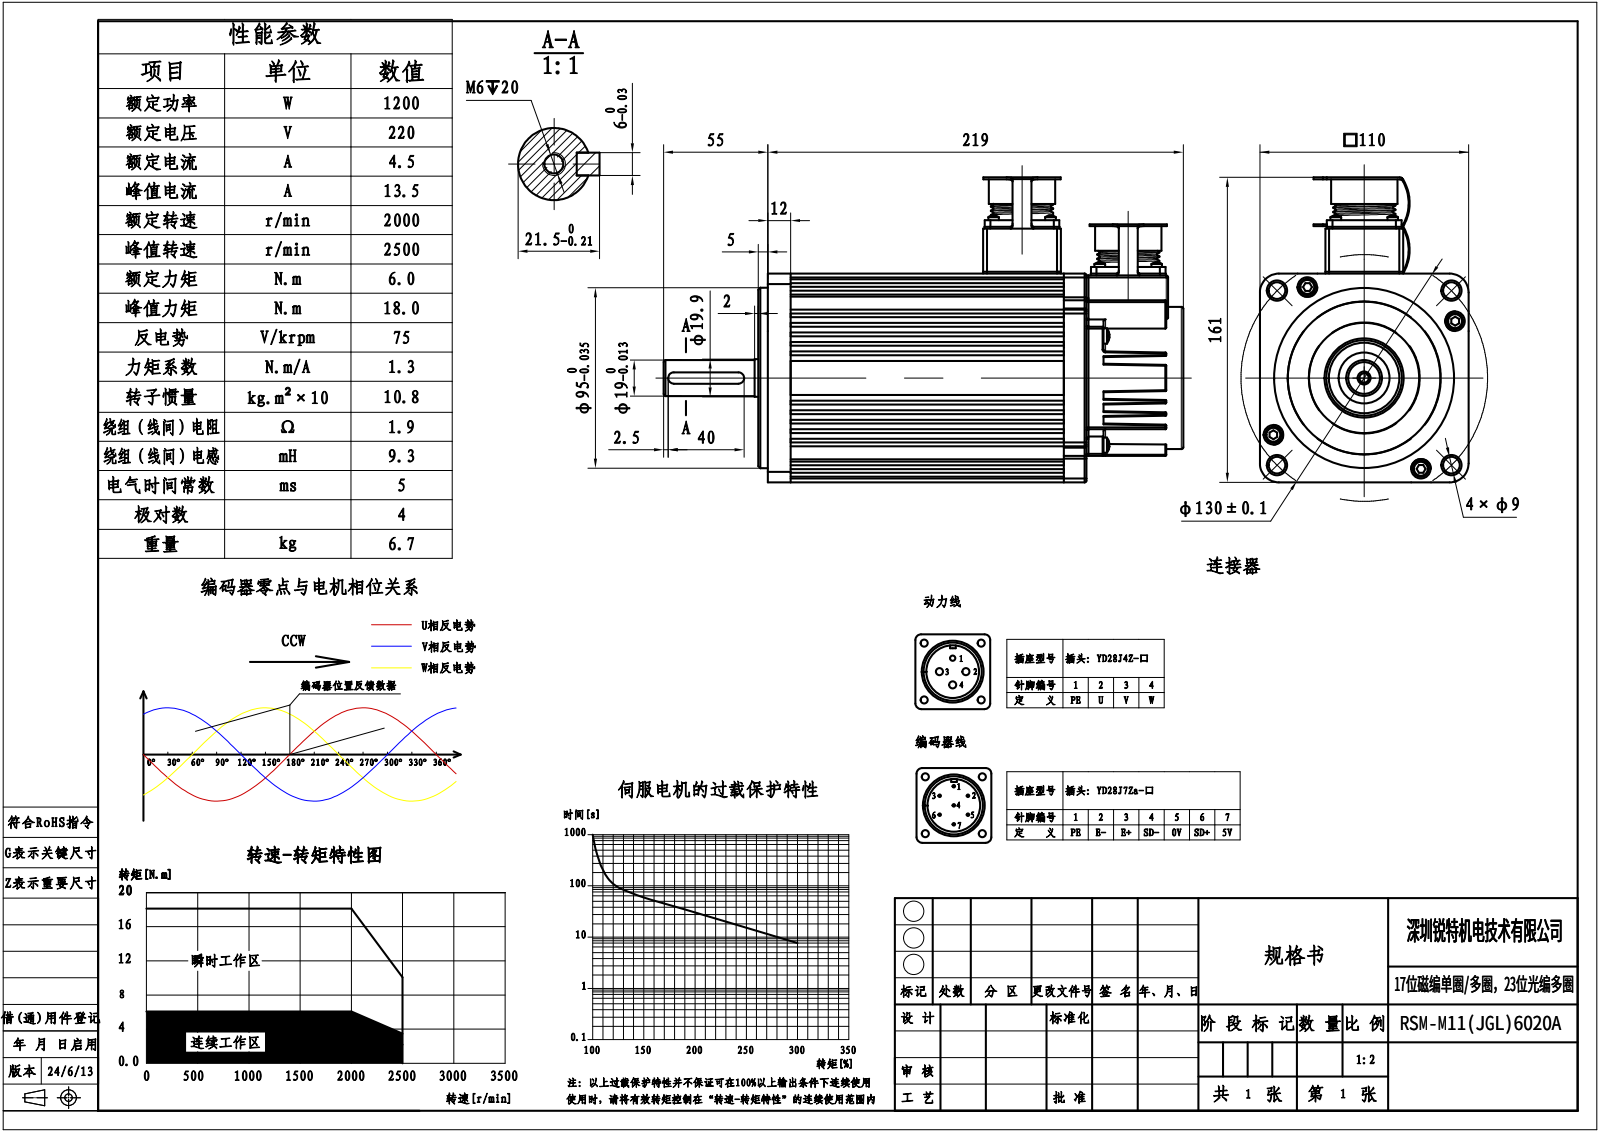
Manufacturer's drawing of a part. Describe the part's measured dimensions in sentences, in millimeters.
The part is named "110后端盖（不带钢套）; 110后端盖（带钢套）; deep groove ball bearings gb_Rolling bearings 6204 GB 276-94; 110编码器罩密封垫 (+5 more)". Its 3-D file was written by "SolidWorks 2018 (CONFIG_CONTROL_DESIGN)". It is 46 solids with 5007 faces: 1494 planar, 2418 cylindrical and 1095 other. Overall it measures 275 by 160.7 by 110 millimeters. Its volume is 826 464 cubic millimeters and its surface area 434 100 square millimeters. Round holes: 15 of diameter 1.5, 11 of diameter 2.5, 8 of diameter 3.5, 8 of diameter 4, 6 of diameter 3.3, 5 of diameter 2, 5 of diameter 4.2, 5 of diameter 5, 4 of diameter 4.5, 4 of diameter 5.6, 4 of diameter 6, 4 of diameter 9. Round bosses or shafts: 15 of diameter 2.5, 13 of diameter 3, 12 of diameter 5.2, 12 of diameter 4.8, 8 of diameter 4, 5 of diameter 7, 4 of diameter 8.8, 4 of diameter 8.6. Partial cylindrical surfaces (rounded edges, fillets, slot ends): 135 of radius 1, 76 of radius 0.5, 37 of radius 2, 34 of radius 3, 9 of radius 1.75, 6 of radius 1.5, 4 of radius 3.75, 4 of radius 10. The main face-to-face distances are 5, 12, 110, 4, 2, 7, 1.5, 3, 63.5, 14. The hole center spacings are 30, 12.5, 17, 18.03, 21.21, 26.63, 29.85, 5.
